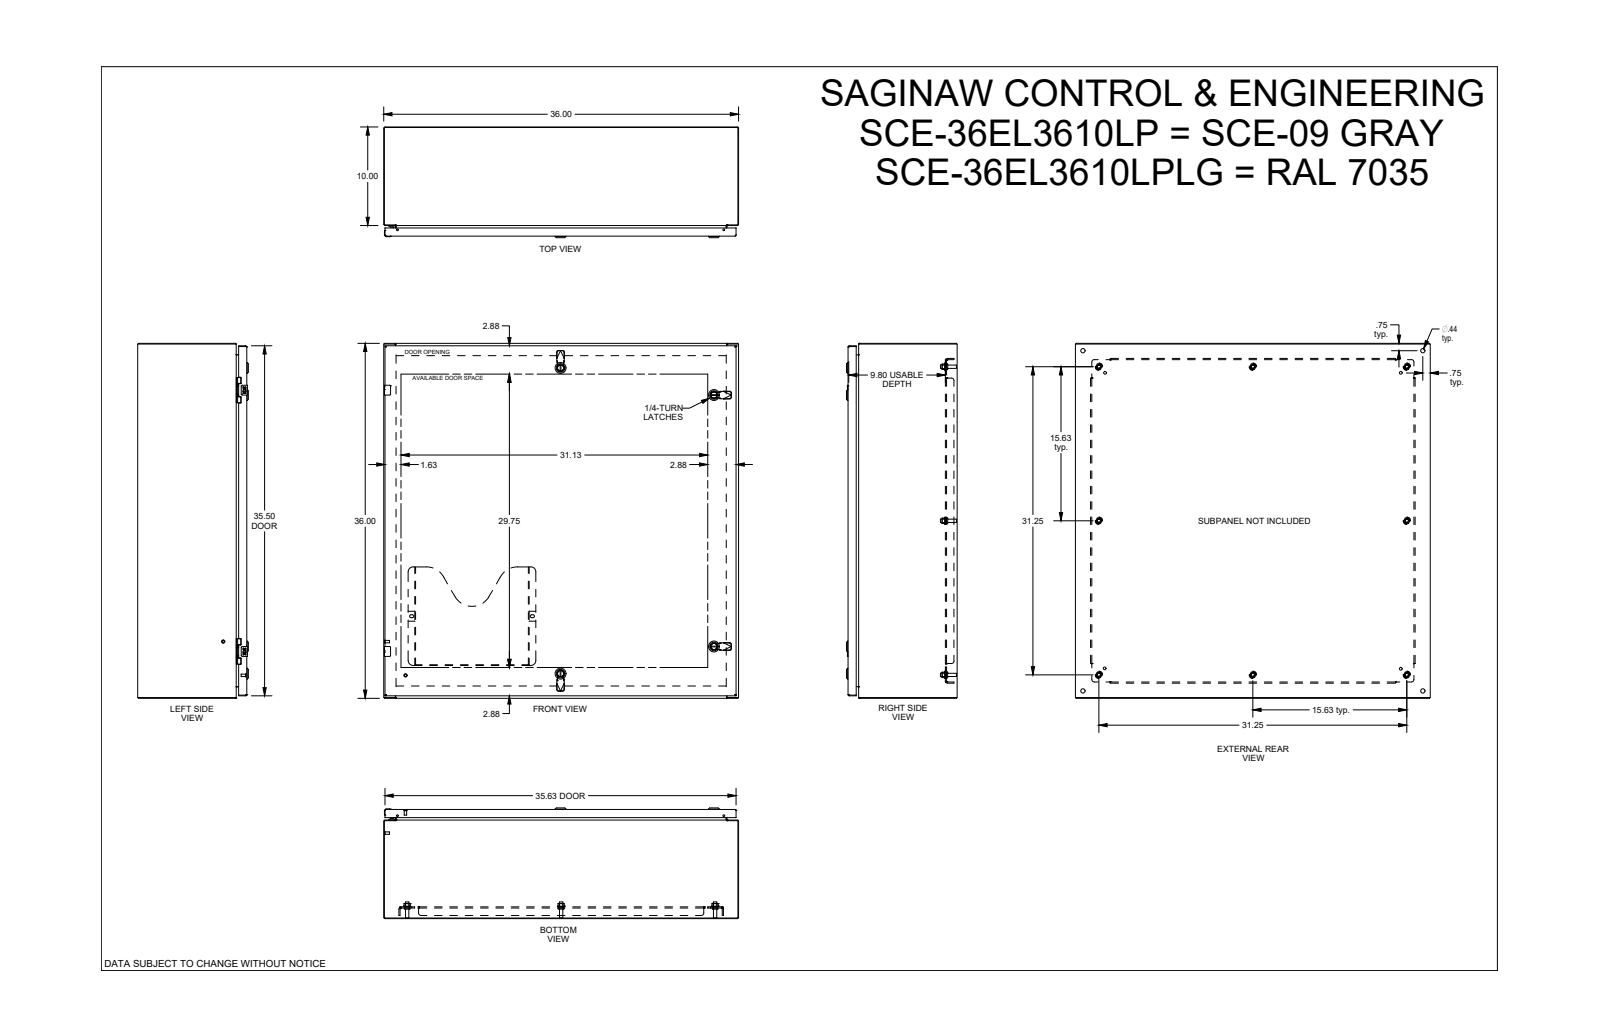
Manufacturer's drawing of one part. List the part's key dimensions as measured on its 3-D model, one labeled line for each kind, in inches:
Part name (STEP PRODUCT): SCE-36EL3610LP
STEP written by: SolidWorks 2021 (AUTOMOTIVE_DESIGN)
Units: inches
Bodies: 65 solids, 3849 faces (1489 planar, 1198 cylindrical, 1162 other)
Overall size (bounding box): 36 × 36 × 11.23
Volume: 497.5 in³ · Surface area: 11 755 in²
Round holes (diameter × count): ⌀0.367 ×8, ⌀0.5 ×8, ⌀0.172 ×4, ⌀0.197 ×4, ⌀0.205 ×4, ⌀0.244 ×4, ⌀0.266 ×4, ⌀0.281 ×4, ⌀0.315 ×4, ⌀0.375 ×4, ⌀0.394 ×4, ⌀0.437 ×4
Round bosses / shafts (diameter × count): ⌀0.366 ×8, ⌀0.332 ×8, ⌀0.17 ×6, ⌀1.102 ×4, ⌀0.78 ×4, ⌀0.63 ×4, ⌀0.531 ×4, ⌀0.504 ×4
Partial cylindrical surfaces — rounded edges, fillets, slot ends (radius × count): R0.012 ×110, R0.01 ×52, R0.02 ×44, R0.015 ×20, R0.04 ×17, R0.157 ×16, R0.06 ×13, R0.029 ×12
Main face-to-face distances: 0.075, 0.075, 35.925, 0.06, 11.073, 10.998, 11.013, 10.938, 1.2, 9.873
Hole centre spacings: 17.326, 37.126, 0.985, 15.019, 26.5, 32.334, 34.11, 0.02
